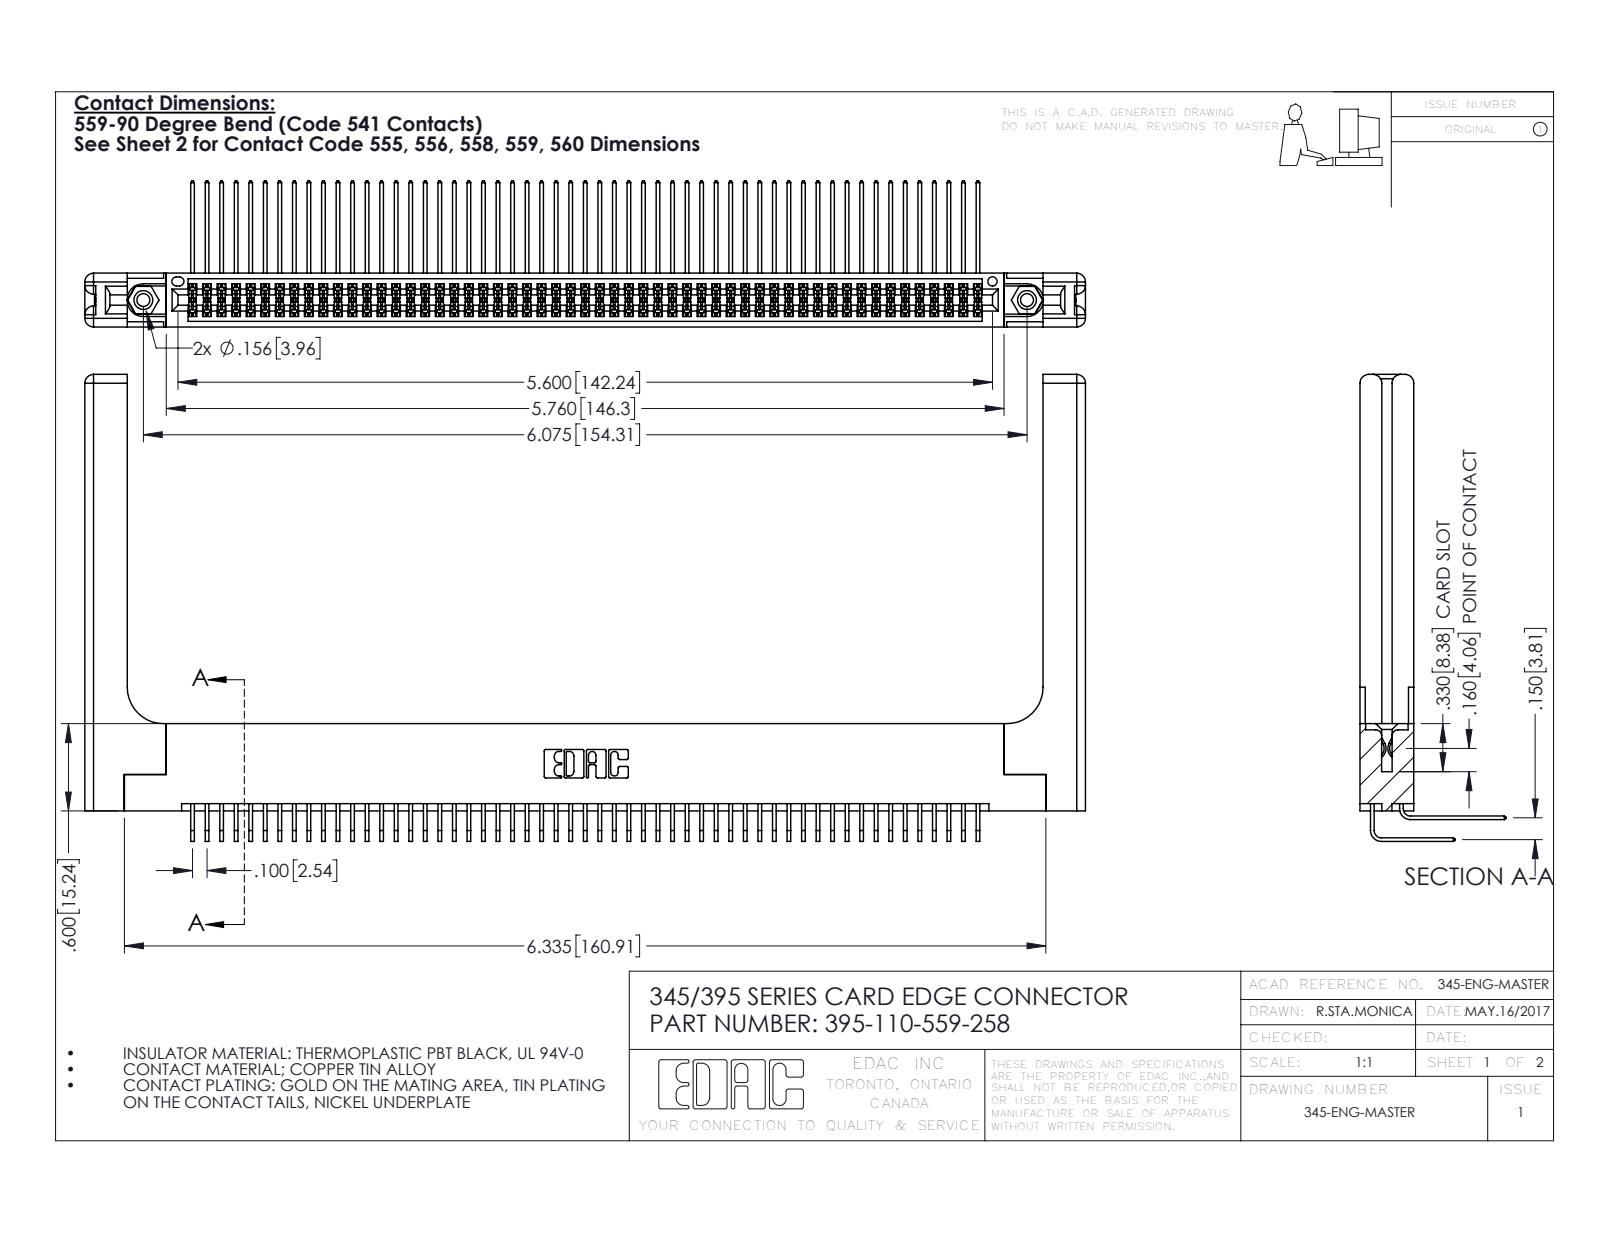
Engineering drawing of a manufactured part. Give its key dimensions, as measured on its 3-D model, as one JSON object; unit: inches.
{"part_name": "345-292-001_558 559 Tail - 1; 345-292-001_559 Tail - 2; 345-250-001_345-250-001-102; 345-220-058_345-220-058 (+2 more)", "step_written_by": "SolidWorks 2016 (CONFIG_CONTROL_DESIGN)", "units": "inches", "bodies": {"solids": 115, "faces": 6102, "planar": 4078, "cylindrical": 1964, "other": 60}, "overall_size": [6.879, 3.209, 1.005], "volume_in3": 1.599, "surface_area_in2": 53.48, "round_holes": [[0.089, 2], [0.125, 2], [0.156, 2], [0.064, 1]], "round_bosses_or_shafts": [[0.155, 2]], "partial_cylinders_radius": [[0.006, 165], [0.01, 22], [0.06, 16], [0.007, 6], [0.031, 6], [0.026, 3], [0.014, 2], [0.019, 2]], "face_to_face_distances": [0.072, 0.298, 0.37, 0.2, 0.098, 0.272, 0.025, 0.225, 0.175, 0.15], "hole_center_spacings": [0.27, 5.839, 6.075]}
